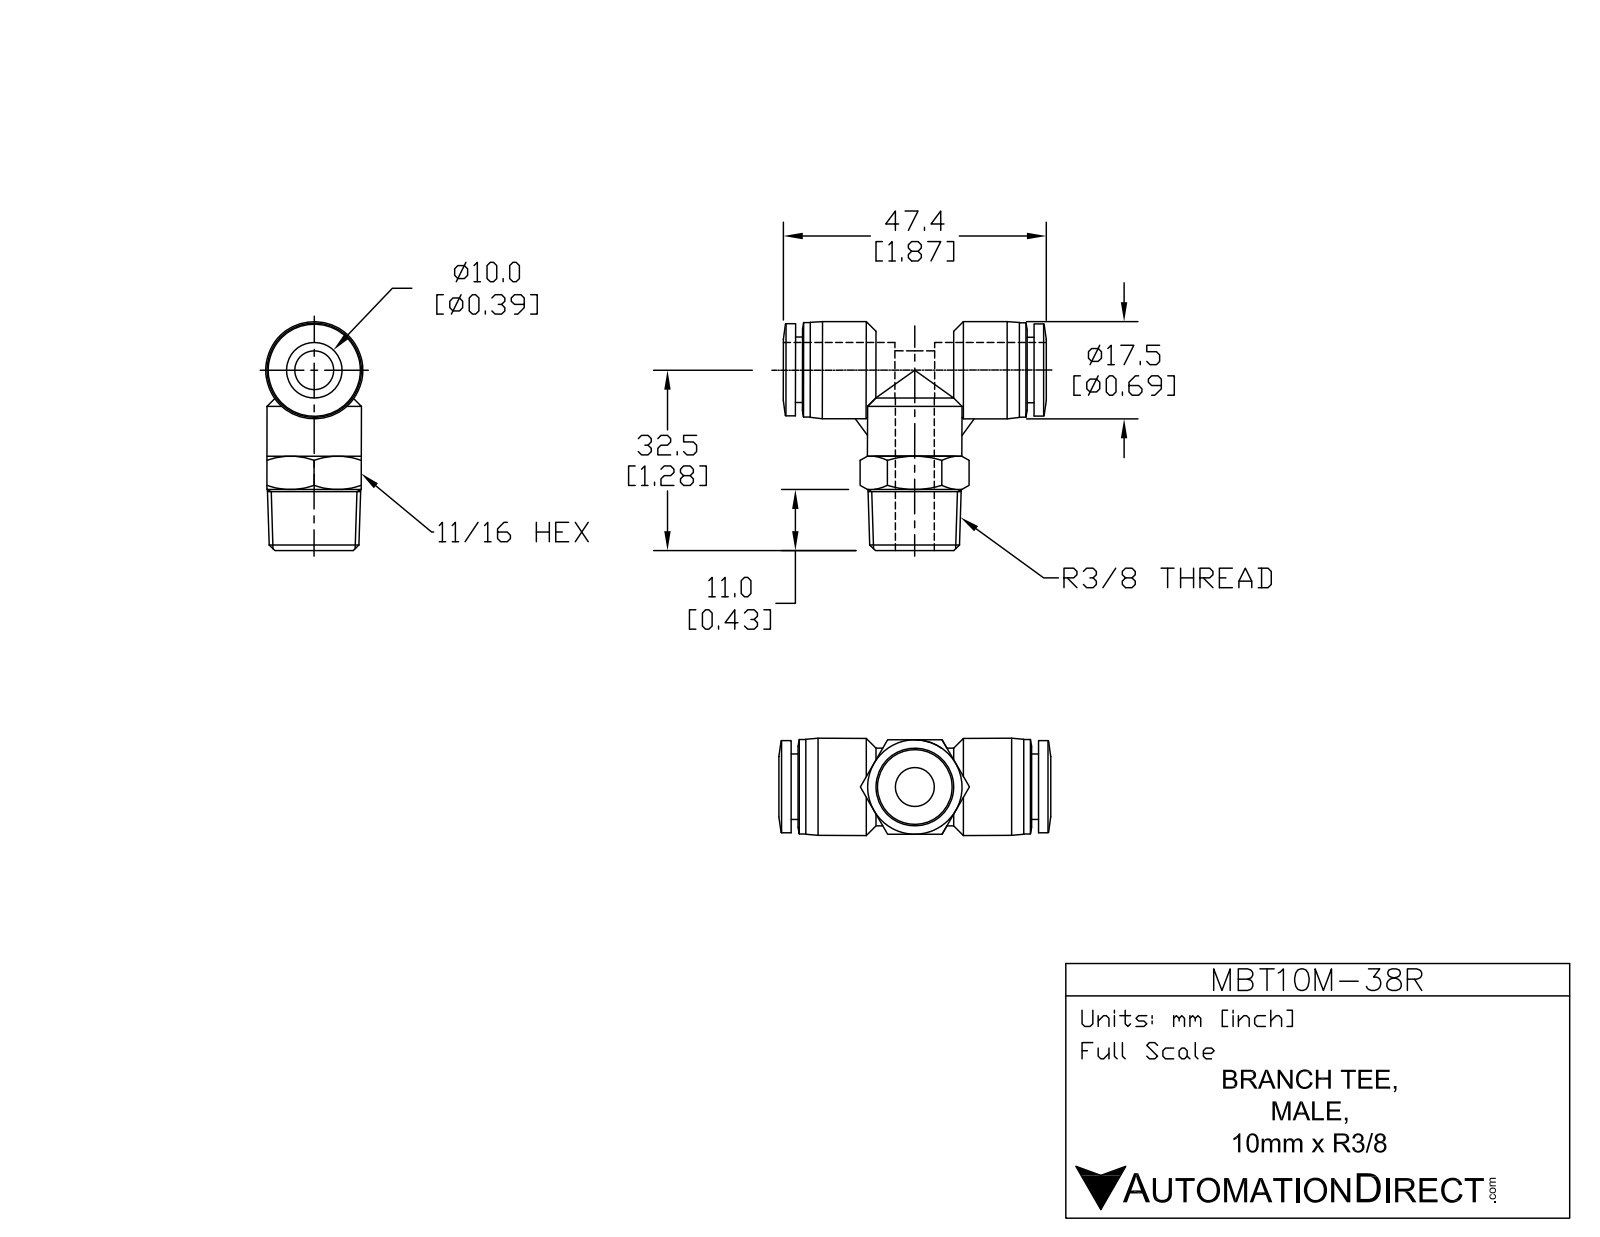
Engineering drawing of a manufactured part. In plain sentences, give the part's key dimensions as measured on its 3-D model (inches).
The part is named "MBT10M-38R". Its 3-D file was written by "SolidWorks 2015 (AUTOMOTIVE_DESIGN)". It is 1 solid with 105 faces: 24 planar, 34 cylindrical and 47 other. Overall it measures 1.98 by 1.624 by 0.689 inches. Its volume is 0.655 cubic inches and its surface area 10.84 square inches. Round holes: 2 of diameter 0.315, 1 of diameter 0.406. Round bosses or shafts: 2 of diameter 0.669, 1 of diameter 0.689, 1 of diameter 0.654, 1 of diameter 0.551, 1 of diameter 0.465. Partial cylindrical surfaces (rounded edges, fillets, slot ends): 1 of radius 0.276. The main face-to-face distances are 0.669, 1.807, 0.709, 1.098, 1.76, 0.047, 0.049, 1.711, 1.758, 0.659.
